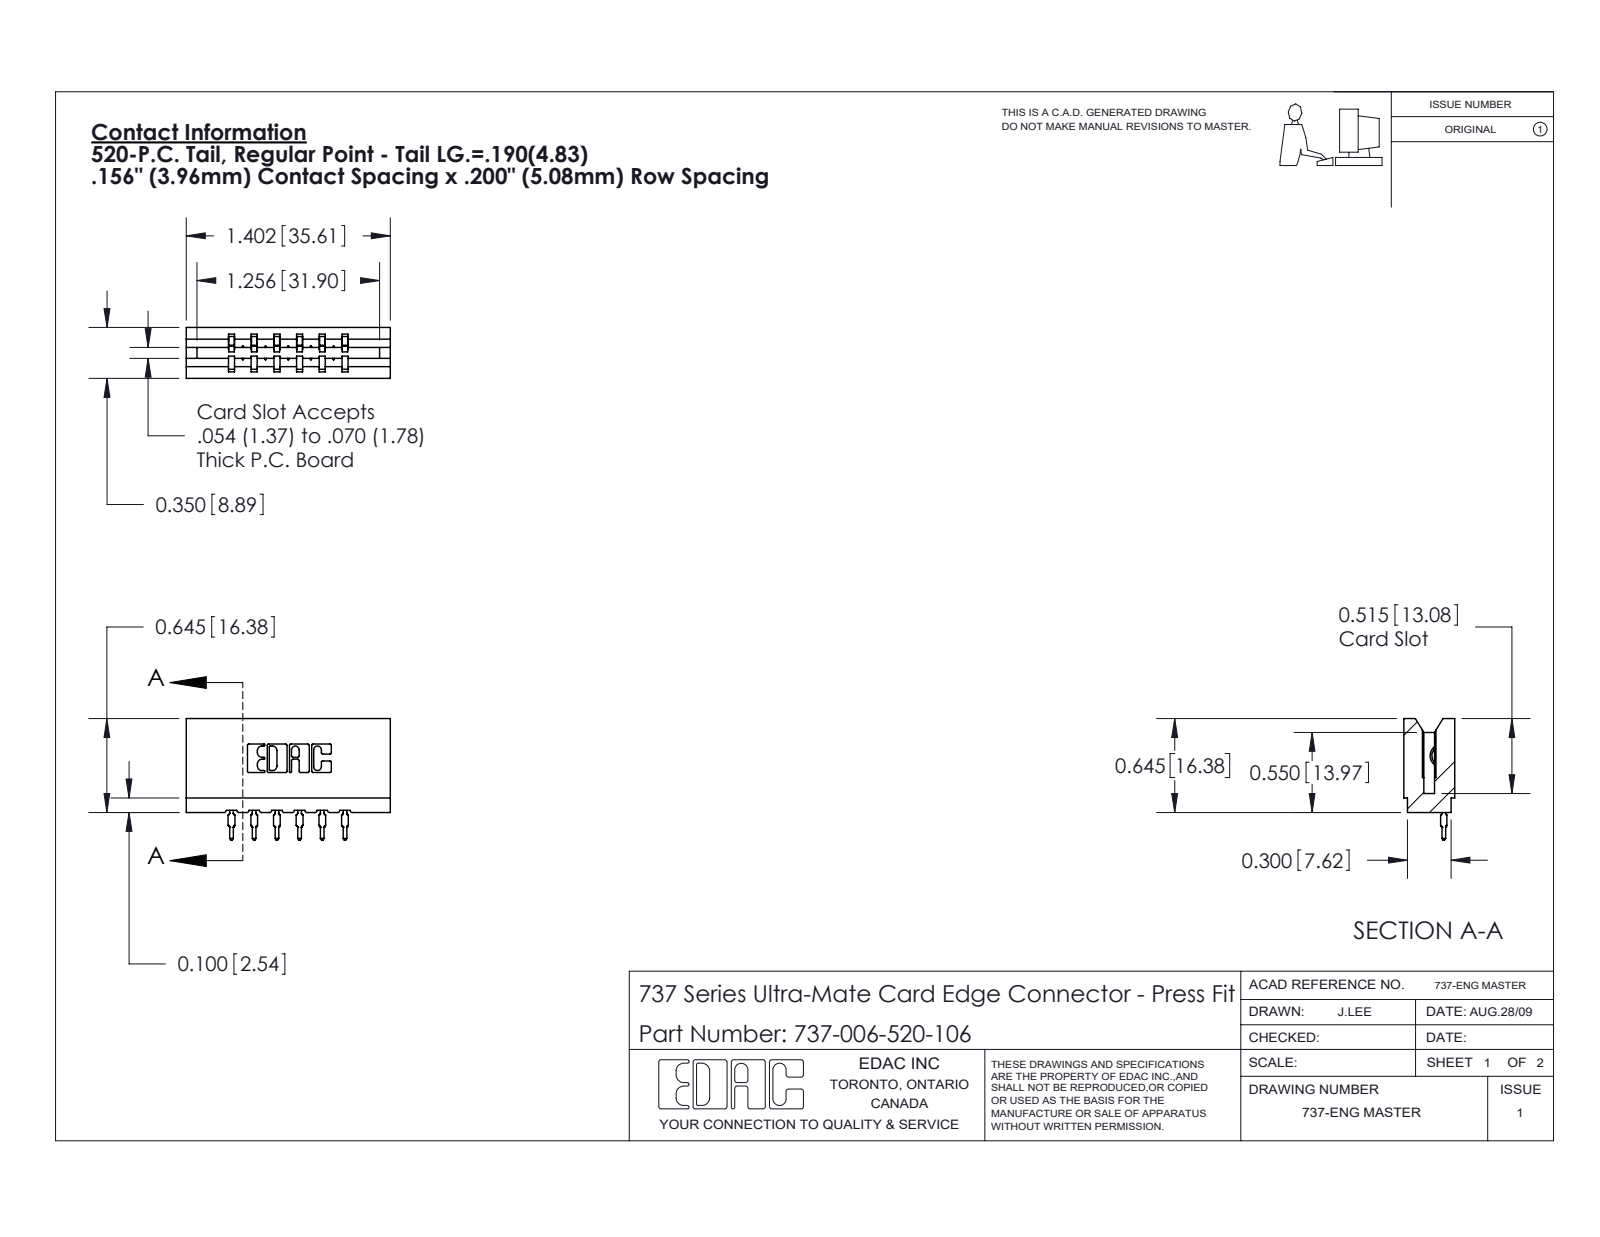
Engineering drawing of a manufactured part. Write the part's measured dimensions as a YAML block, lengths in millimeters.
part_name: "737 Part_Insulator Option - 06; 737-006-520-106; 745-292-001_520"
step_written_by: "SolidWorks 2020 (CONFIG_CONTROL_DESIGN)"
units: millimeters
bodies: {solids: 7, faces: 773, planar: 463, cylindrical: 154, other: 156}
overall_size: [35.6, 21.2, 8.9]
volume: 3670
surface_area: 4223
partial_cylinders:
  - {radius: 0.3, count: 22}
  - {radius: 0.4, count: 12}
  - {radius: 0.5, count: 12}
  - {radius: 0.2, count: 6}
  - {radius: 0.8, count: 6}
  - {radius: 0.1, count: 4}
  - {radius: 0.3, count: 4}
  - {radius: 0.7, count: 3}
face_to_face_distances: [4, 3.5, 5.4, 8.9, 7.9, 9, 5, 1.9, 13, 11.9]
